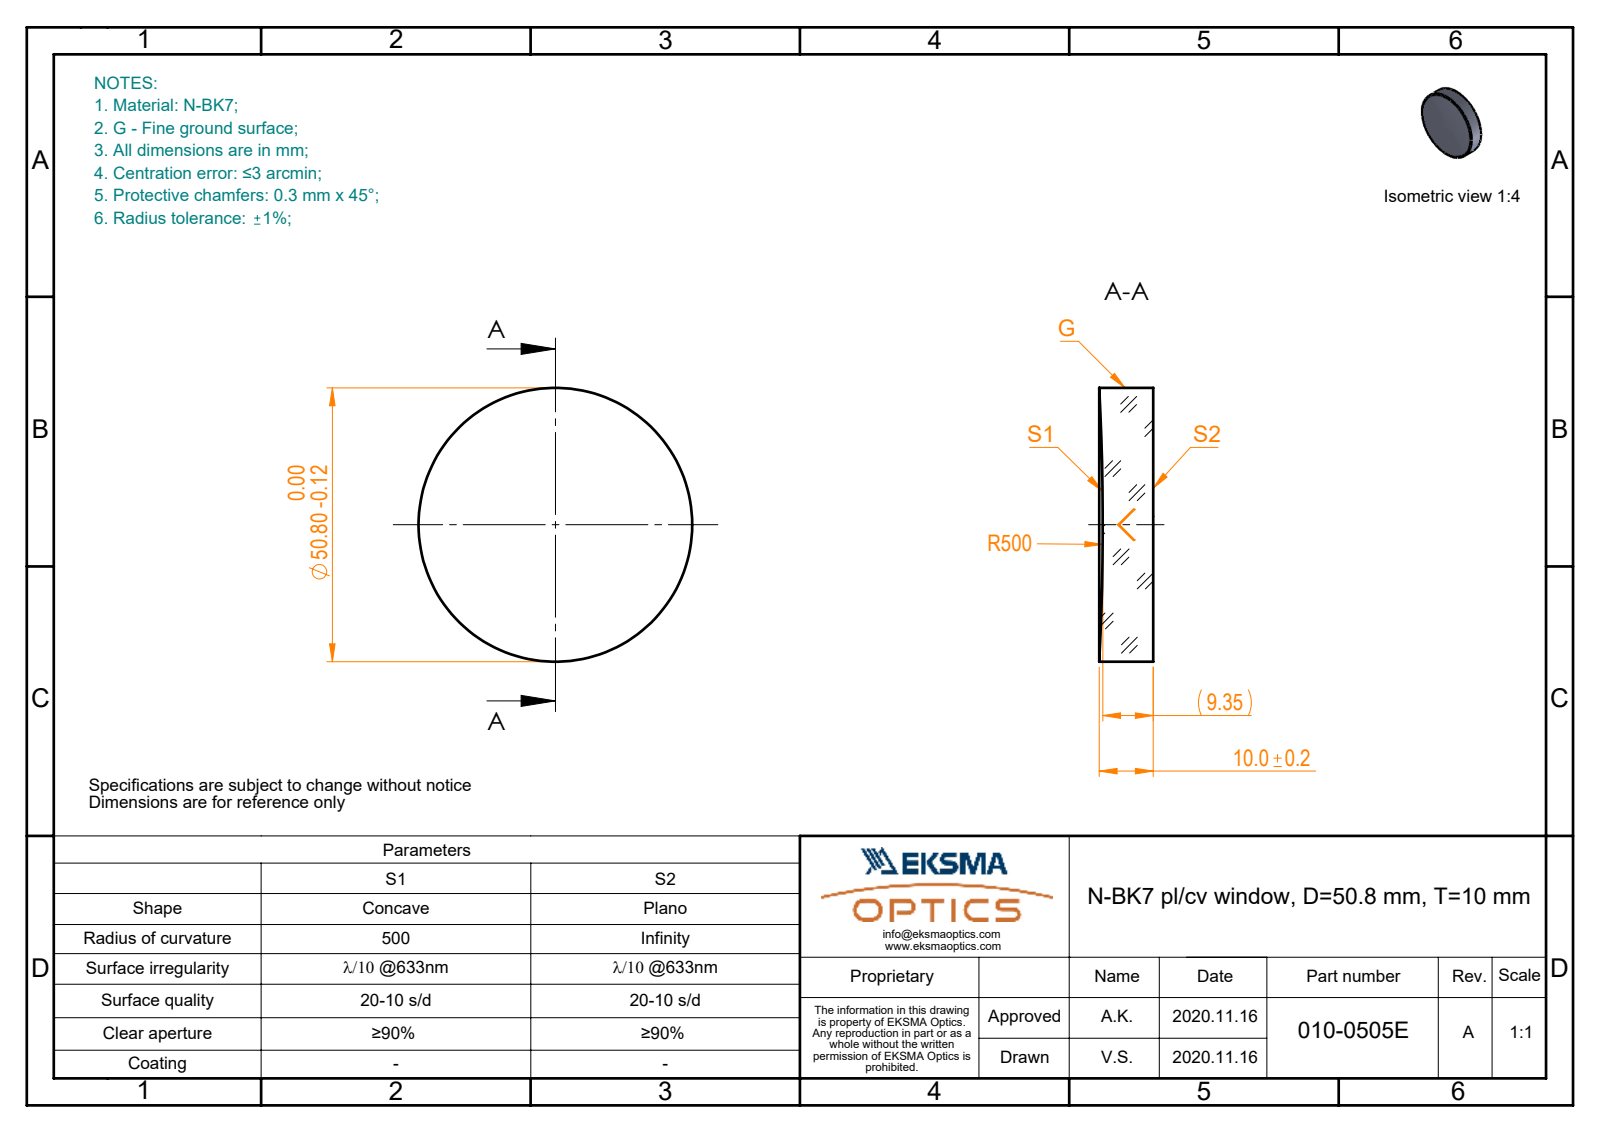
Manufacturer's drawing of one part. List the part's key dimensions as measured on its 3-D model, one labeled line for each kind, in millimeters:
Part name (STEP PRODUCT): 010-0505E_N-BK7_PCV_window
STEP written by: SolidWorks 2019 (CONFIG_CONTROL_DESIGN)
Units: millimetres
Bodies: 1 solid, 5 faces (1 planar, 2 cylindrical, 2 other)
Overall size (bounding box): 50.8 × 50.8 × 10
Volume: 19 614 mm³ · Surface area: 5 651 mm²
Round bosses / shafts (diameter × count): ⌀50.8 ×1
